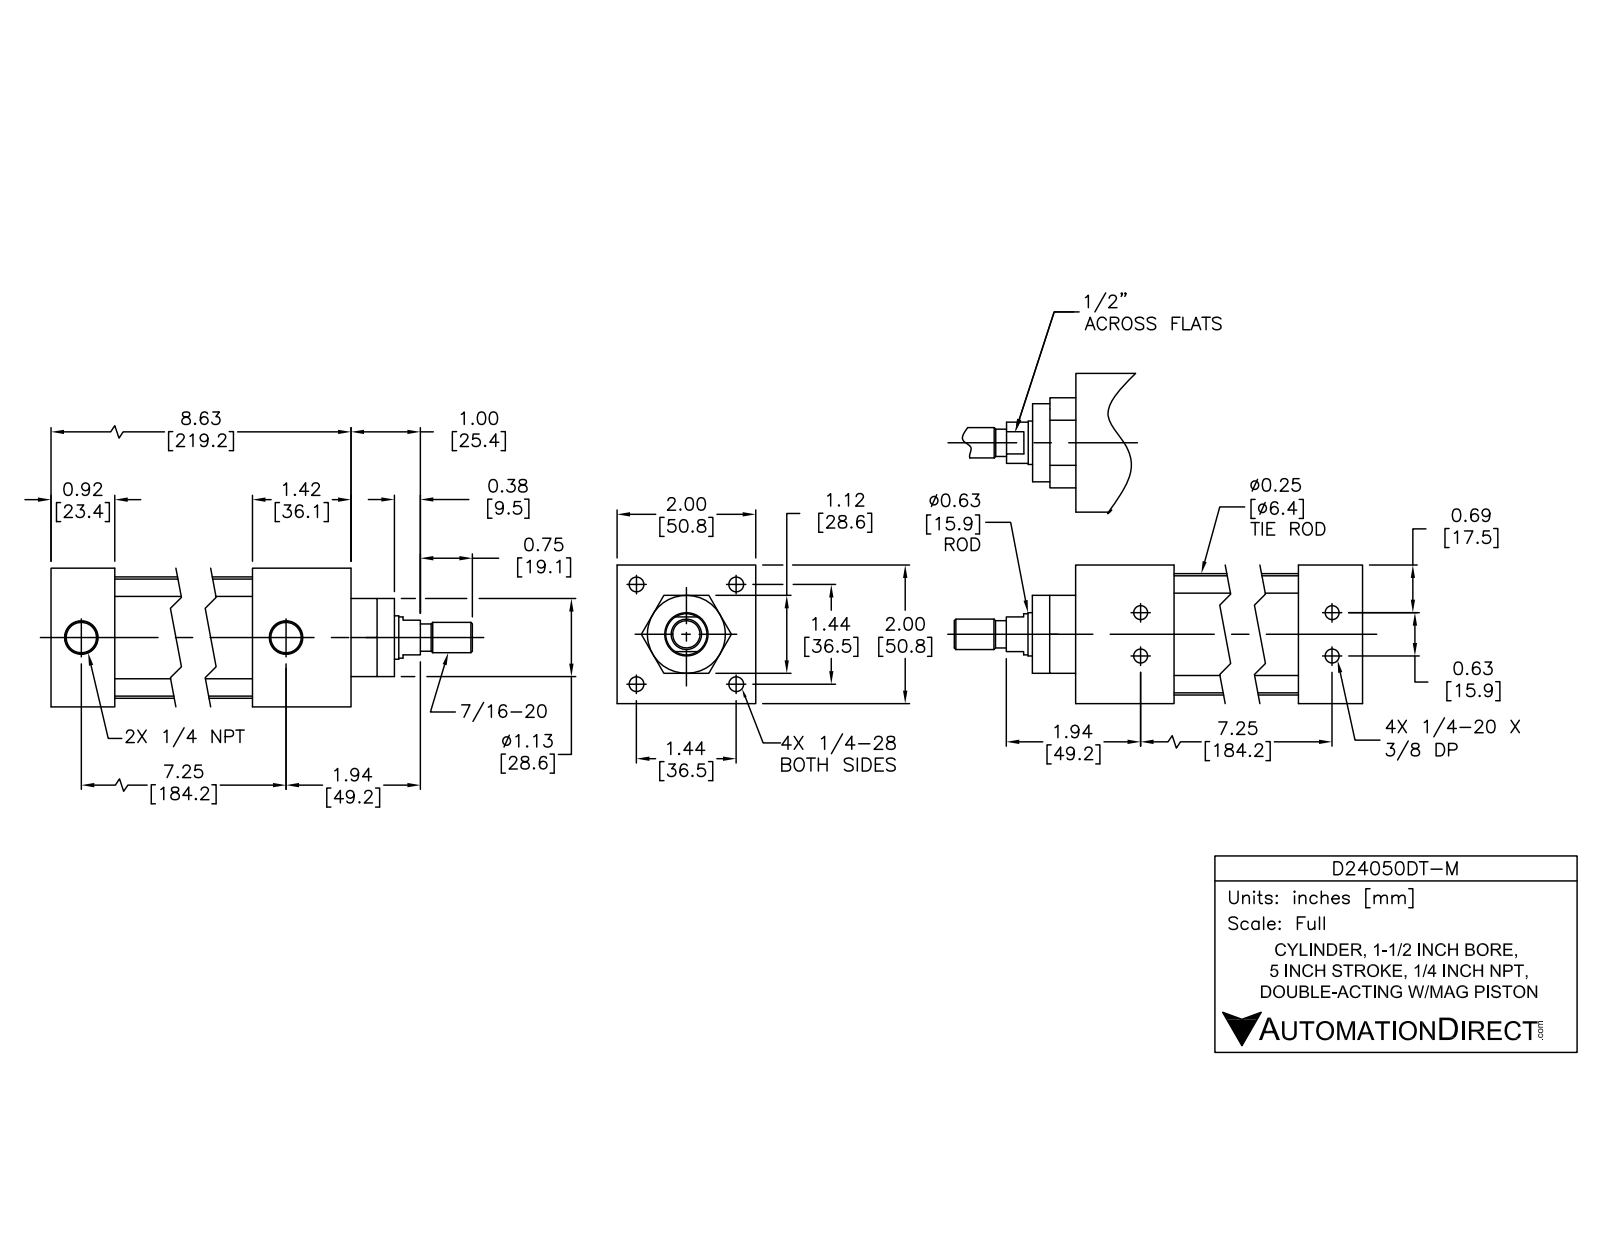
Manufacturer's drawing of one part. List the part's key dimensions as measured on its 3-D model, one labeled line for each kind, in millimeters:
Part name (STEP PRODUCT): D24050DT-M BODY; D24050DT-M; D24050DT-M PISTON
STEP written by: SolidWorks 2015 (AUTOMOTIVE_DESIGN)
Units: millimetres
Bodies: 12 solids, 303 faces (99 planar, 114 cylindrical, 90 other)
Overall size (bounding box): 263.4 × 50.8 × 50.8
Volume: 297 800 mm³ · Surface area: 108 300 mm²
Round holes (diameter × count): ⌀5 ×4, ⌀5.4 ×4, ⌀7.1 ×4, ⌀10.3 ×4, ⌀7.5 ×2, ⌀12.1 ×2, ⌀15.9 ×1, ⌀16 ×1, ⌀38.1 ×1
Round bosses / shafts (diameter × count): ⌀9.9 ×4, ⌀6.4 ×4, ⌀5.6 ×4, ⌀44.5 ×1, ⌀38 ×1, ⌀28.5 ×1, ⌀15.8 ×1, ⌀15 ×1
Partial cylindrical surfaces — rounded edges, fillets, slot ends (radius × count): R5.1 ×4
Main face-to-face distances: 50.8, 219, 36.1, 182.9, 195.6, 159.5, 23.4, 28.5, 193.1, 157
Hole centre spacings: 8, 25.8, 36.4, 15.9, 51.5, 184.1, 184.2, 184.2
